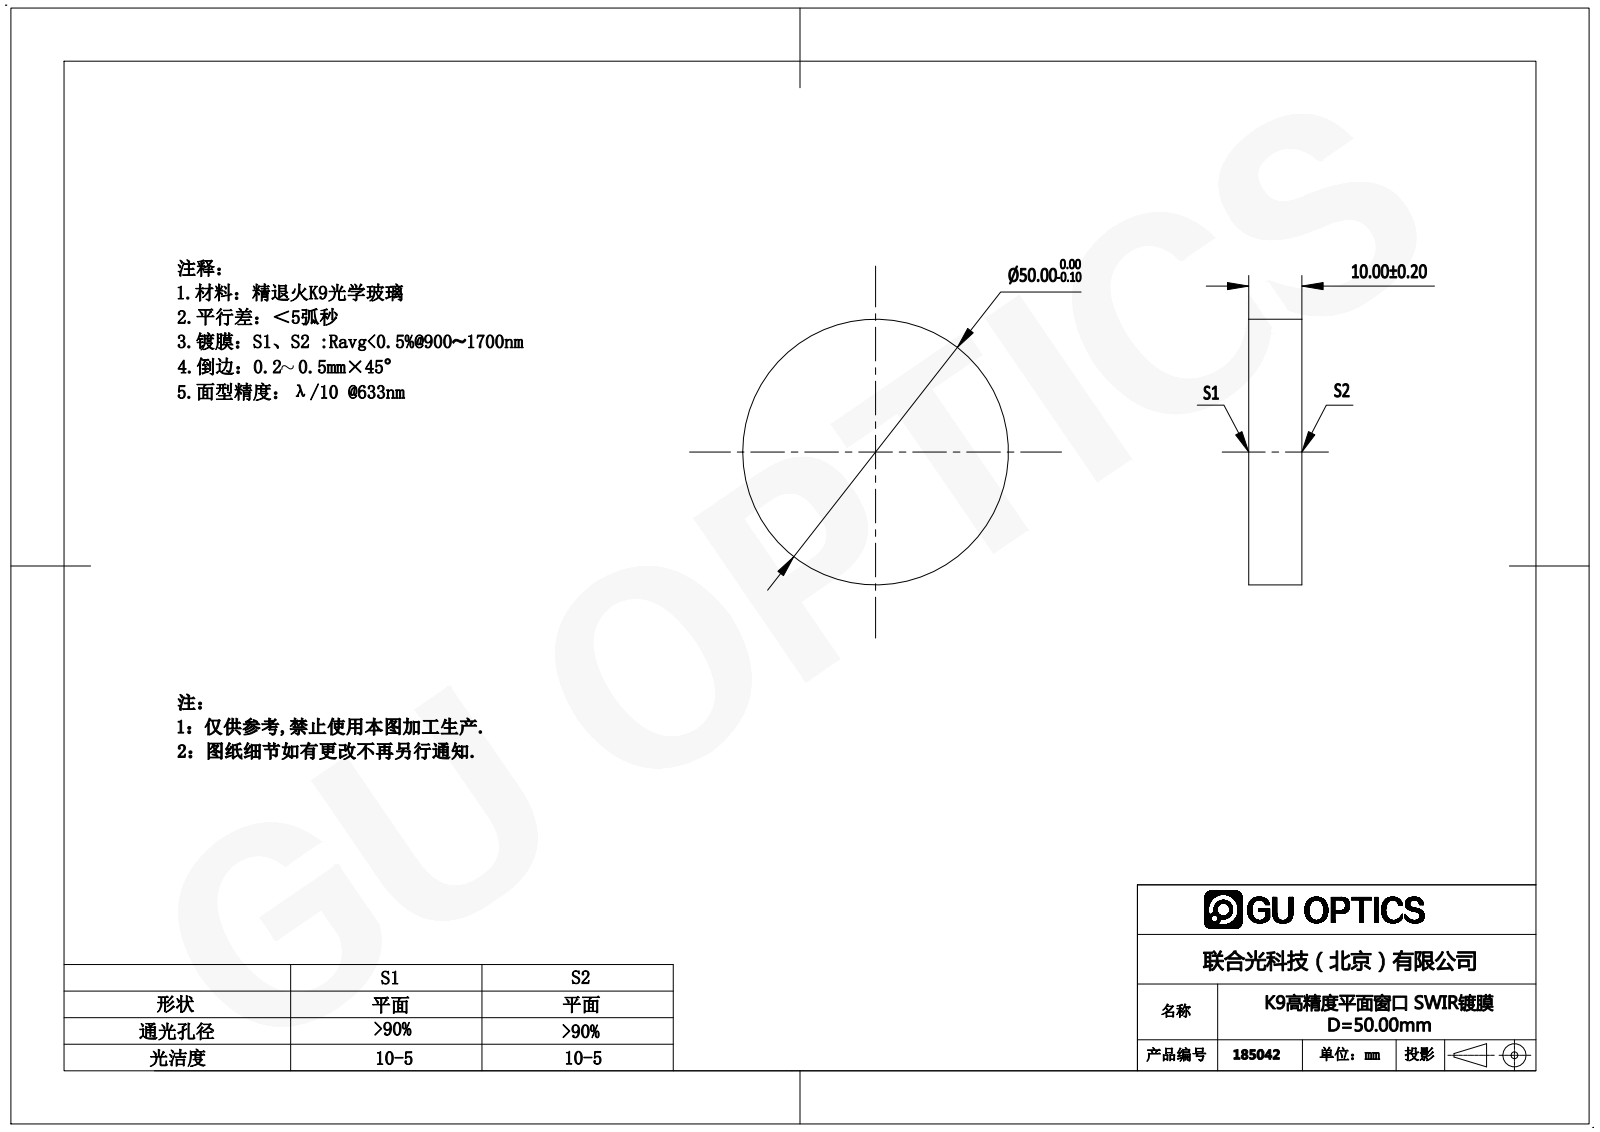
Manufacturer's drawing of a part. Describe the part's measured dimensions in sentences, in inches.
The part is named "185009". Its 3-D file was written by "SolidWorks 2016 (AUTOMOTIVE_DESIGN)". It is 1 solid with 4 faces: 2 planar, 2 cylindrical and 0 other. Overall it measures 1.969 by 1.969 by 0.394 inches. Its volume is 1.198 cubic inches and its surface area 8.522 square inches. Round bosses or shafts: 1 of diameter 1.969. The main face-to-face distances are 0.394.
